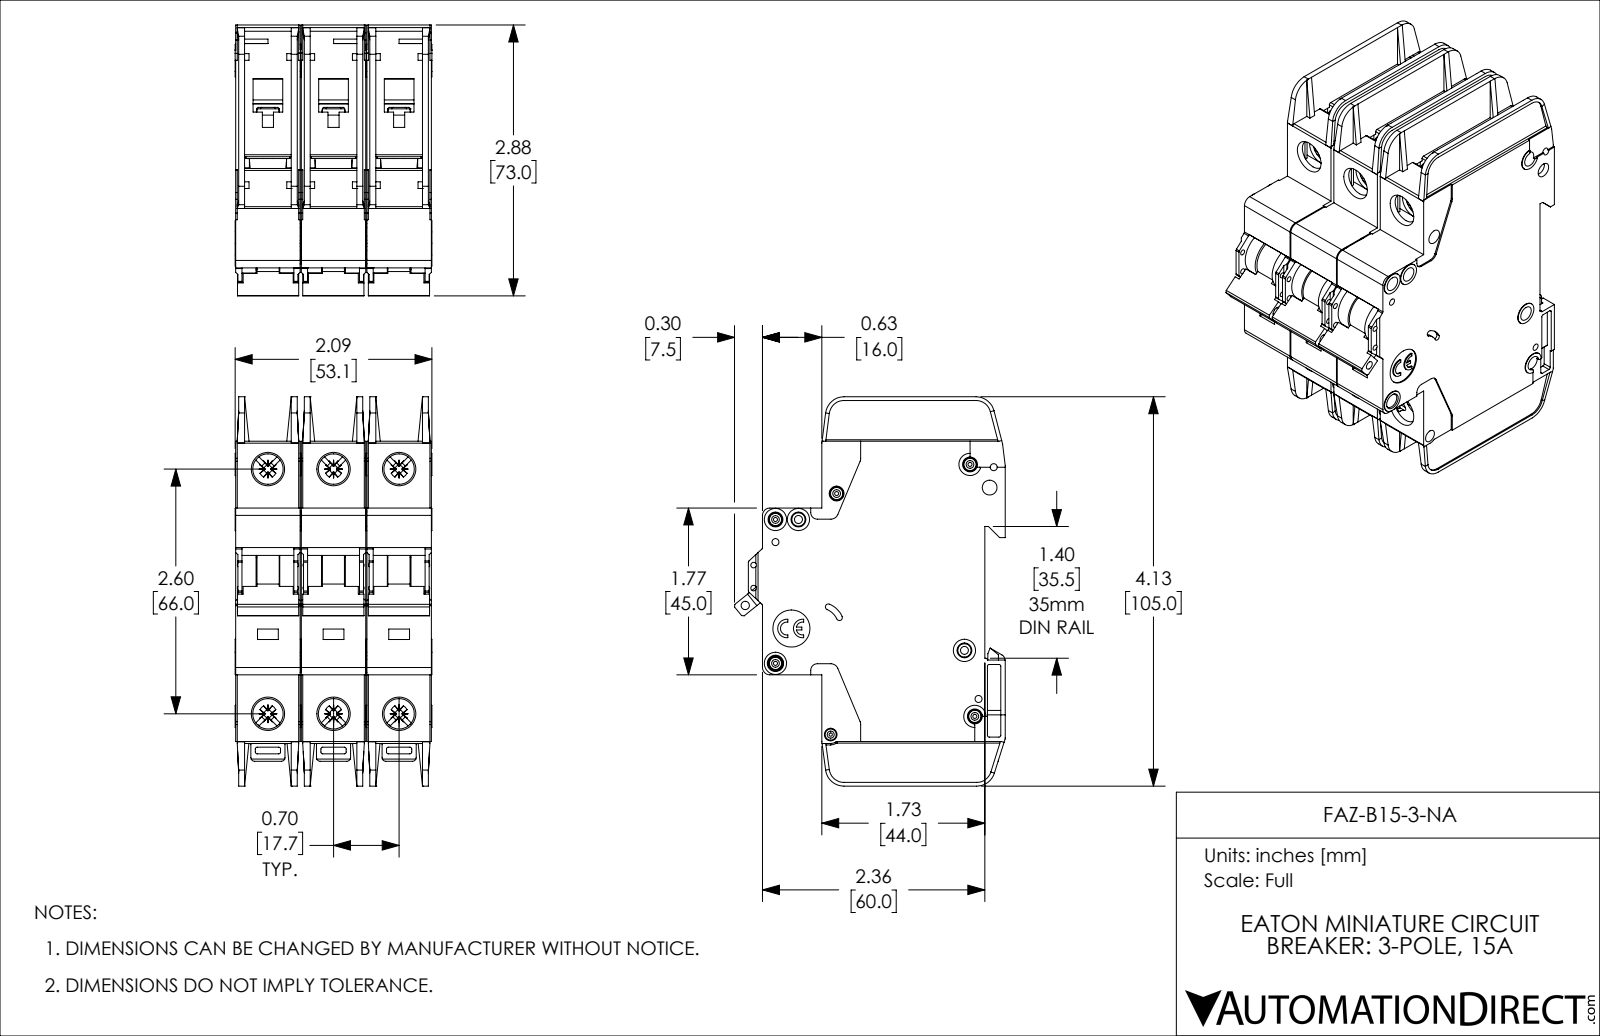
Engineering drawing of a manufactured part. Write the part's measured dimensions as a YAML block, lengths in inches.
part_name: "FAZ-B15-3-NA"
step_written_by: "SolidWorks 2019 (AUTOMOTIVE_DESIGN)"
units: inches
bodies: {solids: 3, faces: 3381, planar: 2013, cylindrical: 1071, other: 297}
overall_size: [4.134, 2.876, 2.091]
volume: 14.05
surface_area: 123
round_holes:
  - {diameter: 0.157, count: 8}
  - {diameter: 0.323, count: 6}
  - {diameter: 0.043, count: 5}
  - {diameter: 0.075, count: 4}
  - {diameter: 0.059, count: 2}
  - {diameter: 0.085, count: 2}
  - {diameter: 0.035, count: 1}
  - {diameter: 0.089, count: 1}
  - {diameter: 0.098, count: 1}
  - {diameter: 0.134, count: 1}
  - {diameter: 0.394, count: 1}
round_bosses_or_shafts:
  - {diameter: 0.13, count: 5}
  - {diameter: 0.236, count: 4}
  - {diameter: 0.118, count: 4}
  - {diameter: 0.098, count: 3}
partial_cylinders:
  - {radius: 0.02, count: 72}
  - {radius: 0.016, count: 30}
  - {radius: 0.039, count: 18}
  - {radius: 0.043, count: 12}
  - {radius: 0.079, count: 12}
  - {radius: 0.008, count: 6}
  - {radius: 0.01, count: 6}
  - {radius: 0.028, count: 6}
face_to_face_distances: [0.697, 0.047, 1.394, 0.685, 0.591, 1.382, 0.744, 0.65, 0.106, 0.094]
hole_center_spacings: [0.697, 2.69, 2.598, 0.244, 0.537, 0.87, 1.394, 2.948]
